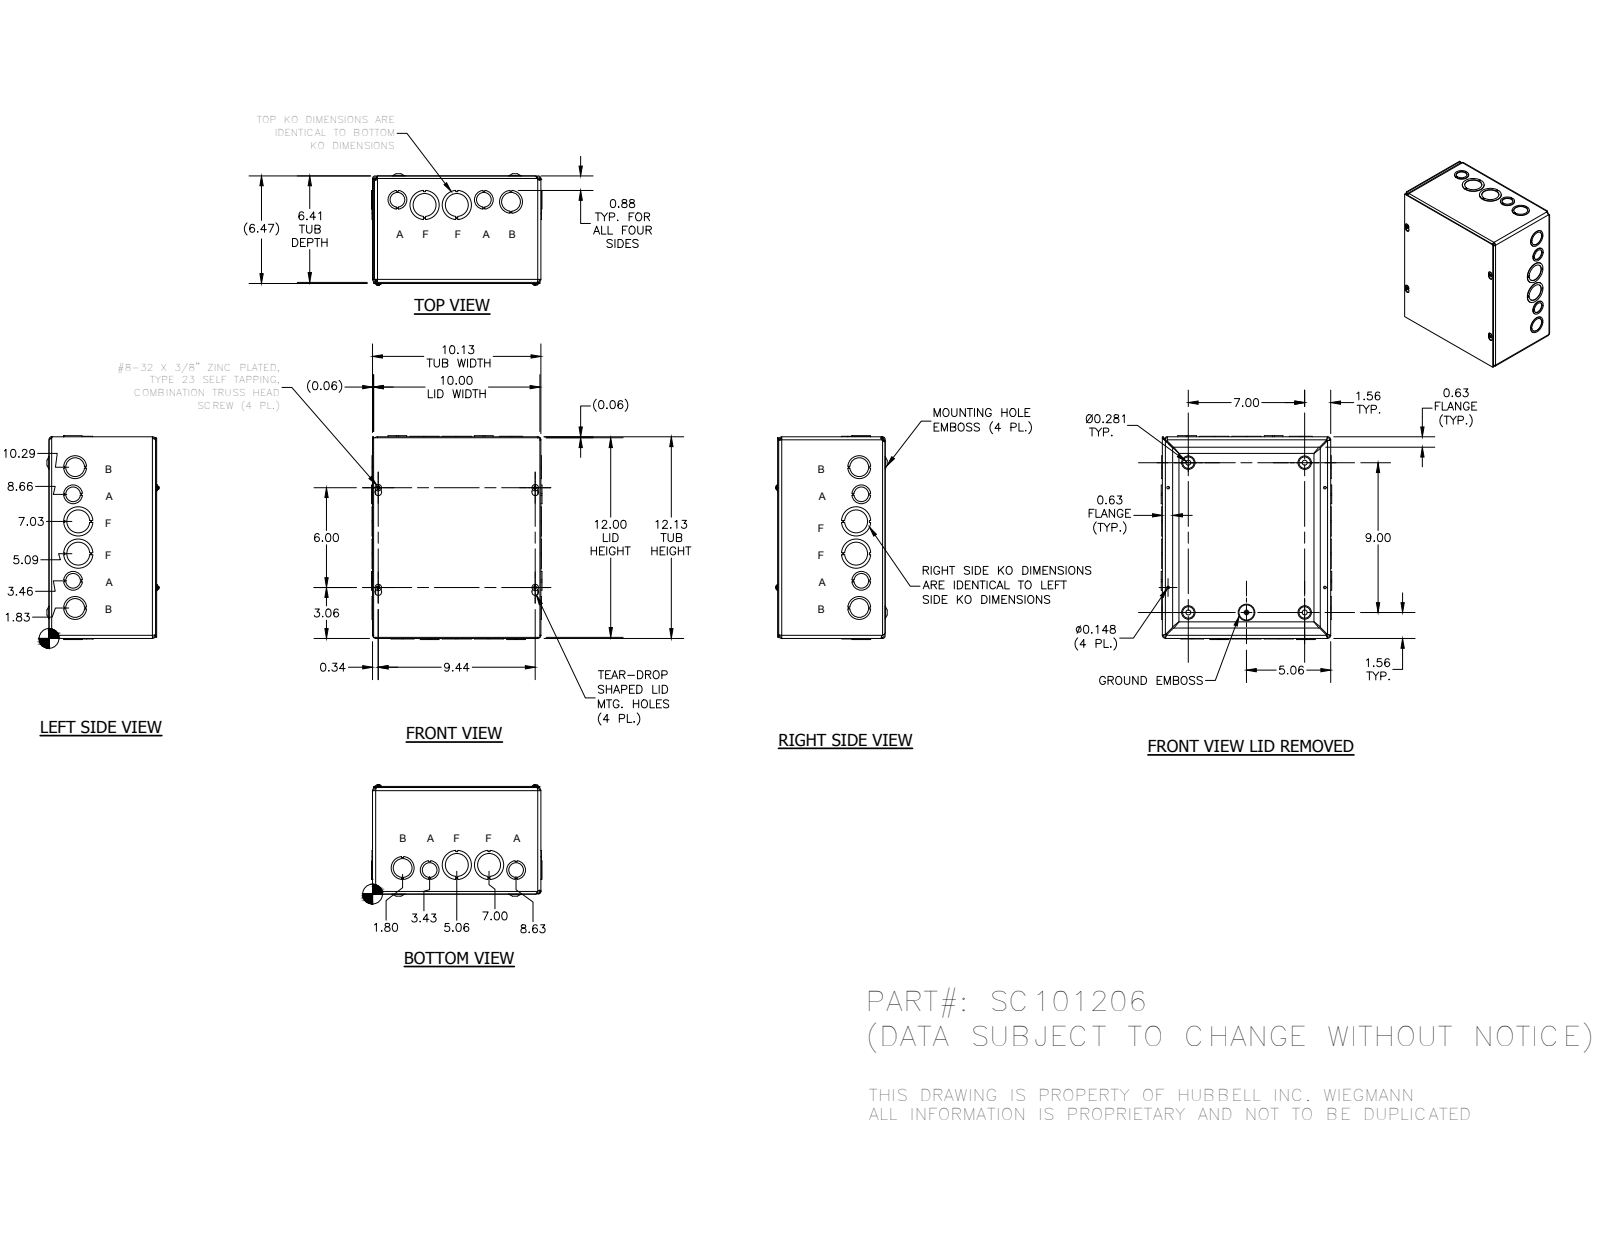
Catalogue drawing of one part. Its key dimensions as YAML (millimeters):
part_name: "SC1012BKP; SC101206WRA; SC1012LID; 34056 (+1 more)"
step_written_by: "Autodesk Inventor 2014 (AUTOMOTIVE_DESIGN)"
units: millimeters
bodies: {solids: 22, faces: 974, planar: 617, cylindrical: 199, other: 158}
overall_size: [311.12, 260.32, 170]
round_holes:
  - {diameter: 28.57, count: 10}
  - {diameter: 34.92, count: 9}
  - {diameter: 22.22, count: 6}
  - {diameter: 44.45, count: 5}
  - {diameter: 3.76, count: 4}
  - {diameter: 7.62, count: 4}
  - {diameter: 4.19, count: 1}
round_bosses_or_shafts:
  - {diameter: 9.75, count: 4}
  - {diameter: 4.17, count: 4}
  - {diameter: 5.8, count: 1}
partial_cylinders:
  - {radius: 3.17, count: 12}
  - {radius: 4.75, count: 8}
  - {radius: 1.4, count: 4}
  - {radius: 1.57, count: 4}
  - {radius: 2.38, count: 4}
  - {radius: 2.97, count: 4}
  - {radius: 3.15, count: 4}
  - {radius: 3.96, count: 4}
face_to_face_distances: [1.57, 161.12, 1.58, 162.69, 1.59, 162.71, 164.28, 257.18, 255.6, 255.61]
hole_center_spacings: [42.15, 91.03, 49.09, 49.28, 132.17, 193, 282.61, 41.52]
